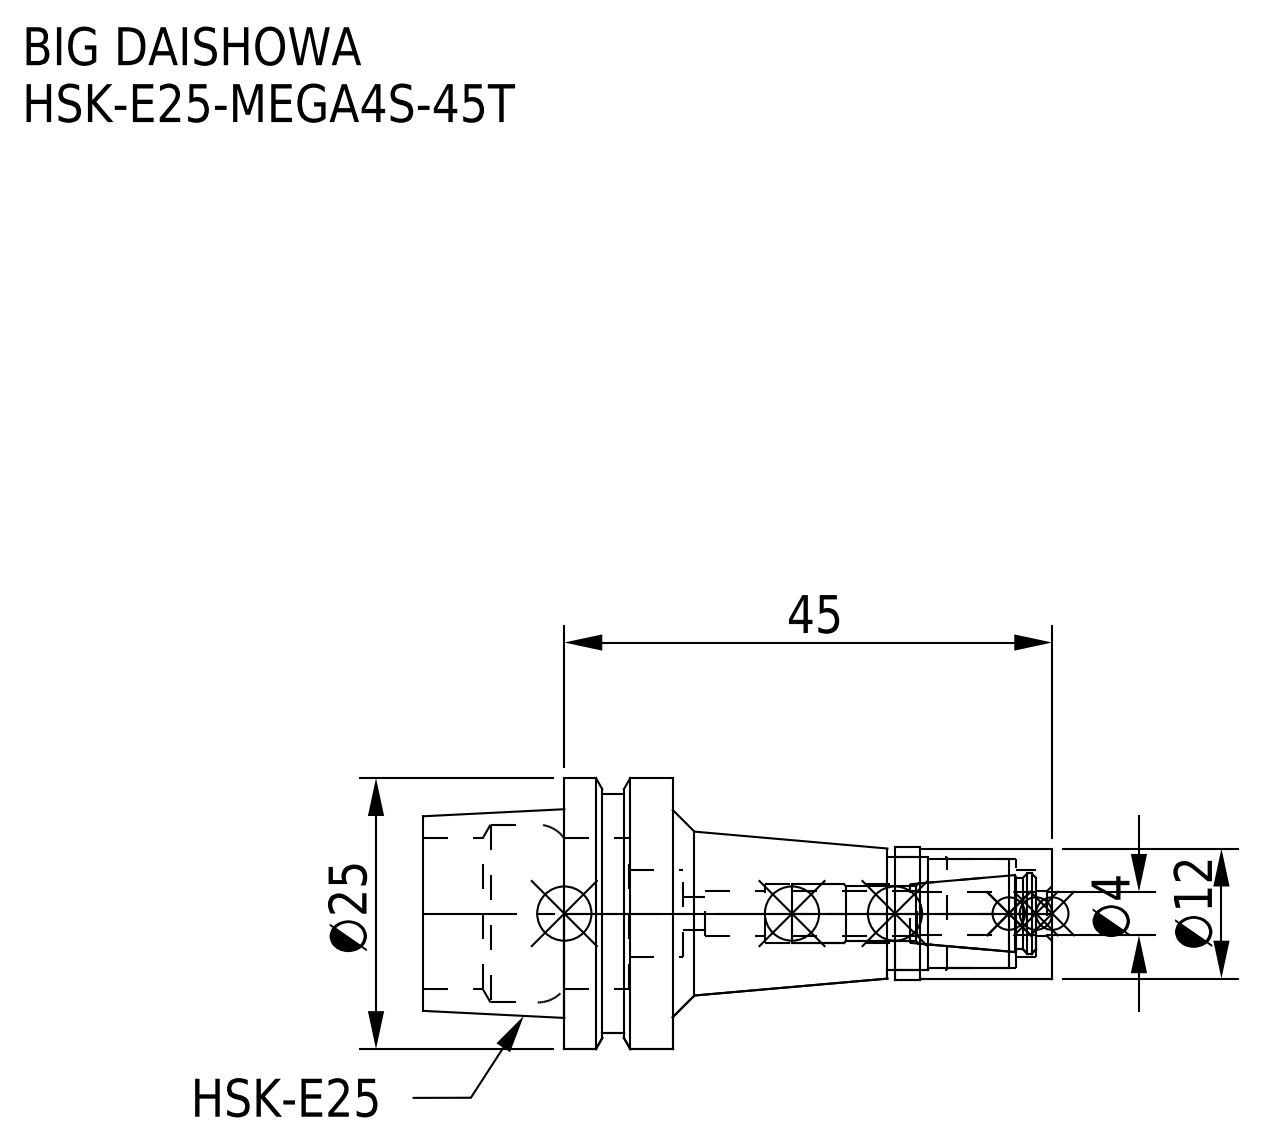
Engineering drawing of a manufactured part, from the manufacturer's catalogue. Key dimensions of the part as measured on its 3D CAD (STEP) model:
Part name (STEP PRODUCT): HSK-E25-MEGA4S-45T-040.stp; HSK-E25-MEGA4S-45T; HE25MS04045T-040_ASM.stp; HSK-E25-MEGA4S-45T_1.stp (+3 more)
STEP written by: SolidWorks 2019 (CONFIG_CONTROL_DESIGN)
Units: millimetres
Bodies: 2 solids, 74 faces (18 planar, 38 cylindrical, 18 other)
Overall size (bounding box): 58 × 25 × 25
Volume: 8 544 mm³ · Surface area: 6 427 mm²
Round holes (diameter × count): ⌀3 ×1, ⌀4.1 ×1, ⌀4.2 ×1, ⌀5.4 ×1, ⌀8 ×1, ⌀10 ×1, ⌀10.5 ×1, ⌀14 ×1, ⌀16.4 ×1
Round bosses / shafts (diameter × count): ⌀25 ×1, ⌀22 ×1, ⌀12.3 ×1, ⌀12 ×1
Main face-to-face distances: 10, 13, 4.05, 5.95, 23, 18.95, 35, 39.05, 45, 58
